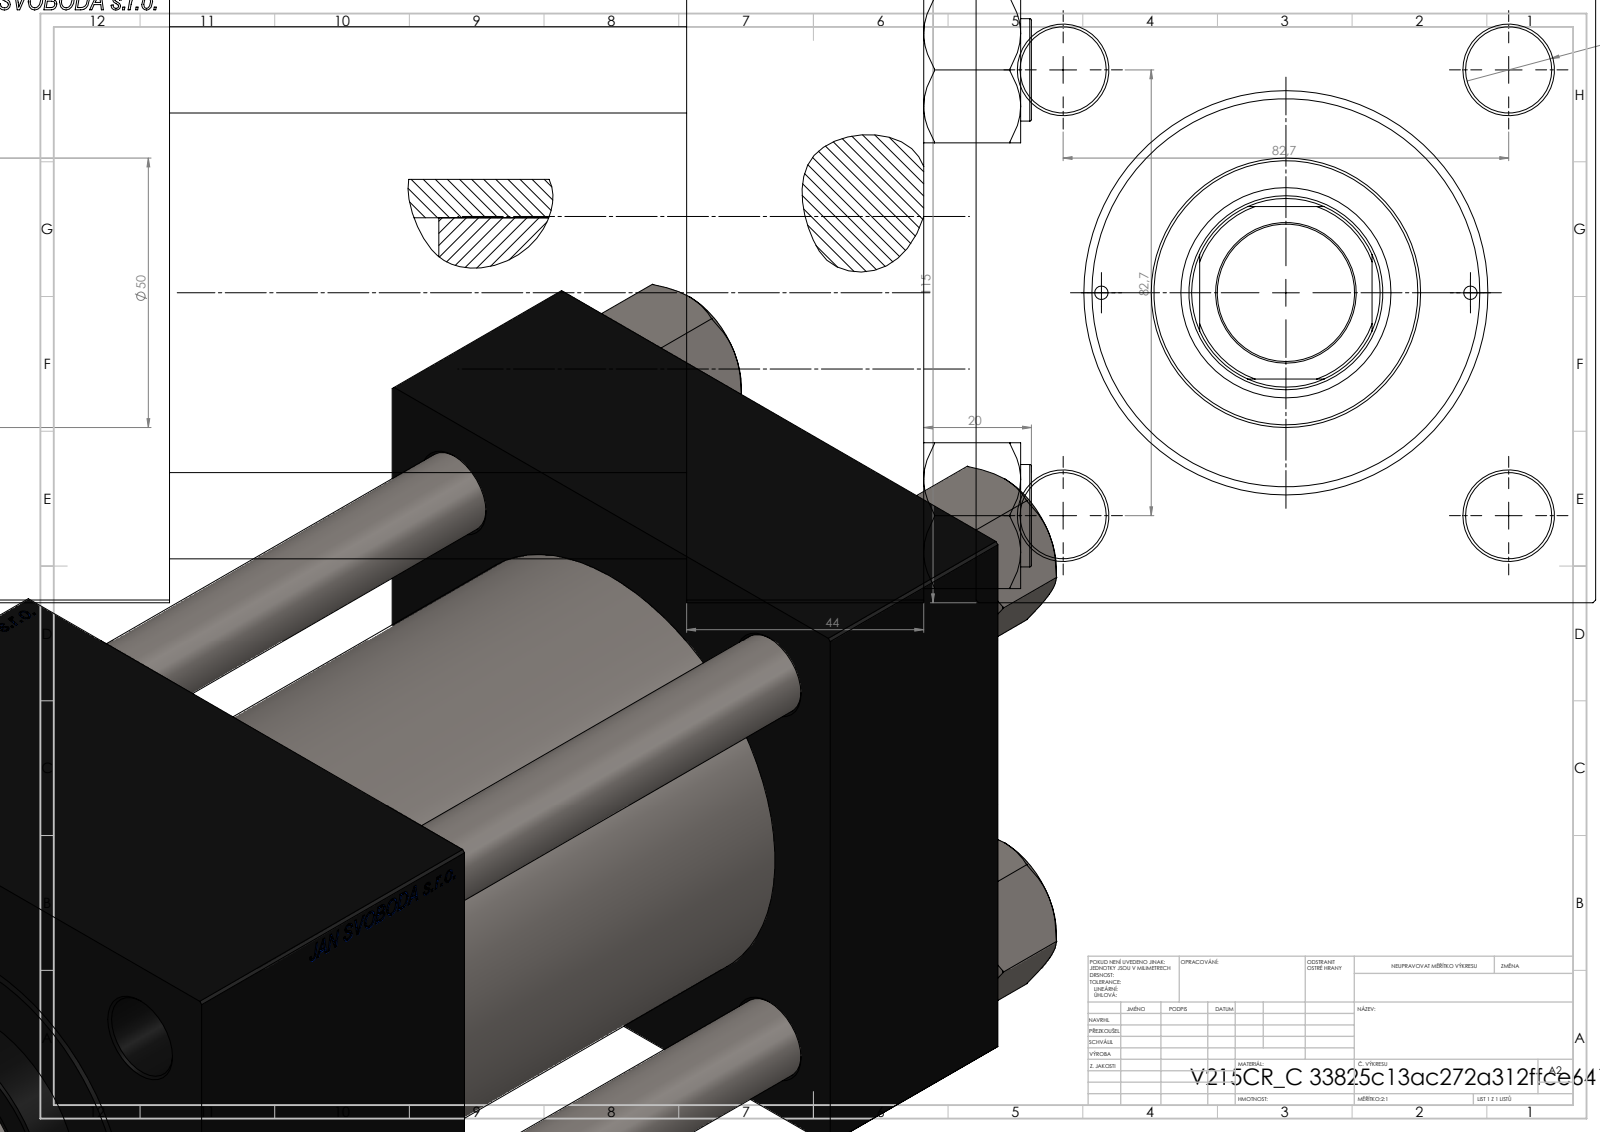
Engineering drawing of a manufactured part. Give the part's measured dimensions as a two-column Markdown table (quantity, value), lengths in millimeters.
| quantity | value |
| --- | --- |
| part name | NUT_M5_C; V215_VC_A; V215CR_VCP_C; V215CR_C_Body (+1 more) |
| STEP written by | SolidWorks 2019 (CONFIG_CONTROL_DESIGN) |
| units | millimeters |
| bodies | 11 solids, 1202 faces (576 planar, 90 cylindrical, 536 other) |
| overall size | 260 × 115 × 115 |
| volume | 1 865 000 mm³ |
| surface area | 293 582 mm² |
| round holes (diameter × count) | 16 × 4, 2.5 × 2, 7 × 2, 26.44 × 2, 35 × 2, 25.5 × 1, 36 × 1, 39 × 1, 61 × 1, 72 × 1, 80 × 1 |
| round bosses / shafts (diameter × count) | 19 × 4, 86 × 1, 50 × 1 |
| partial cylindrical surfaces (radius × count) | 17.5 × 1 |
| main face-to-face distances | 115, 44, 209, 165, 140, 96, 69, 180.3, 136.3, 40.3 |
| hole center spacings | 41.96, 58.48, 82.7, 86.17, 34.25, 116.96, 68.5, 141 |
